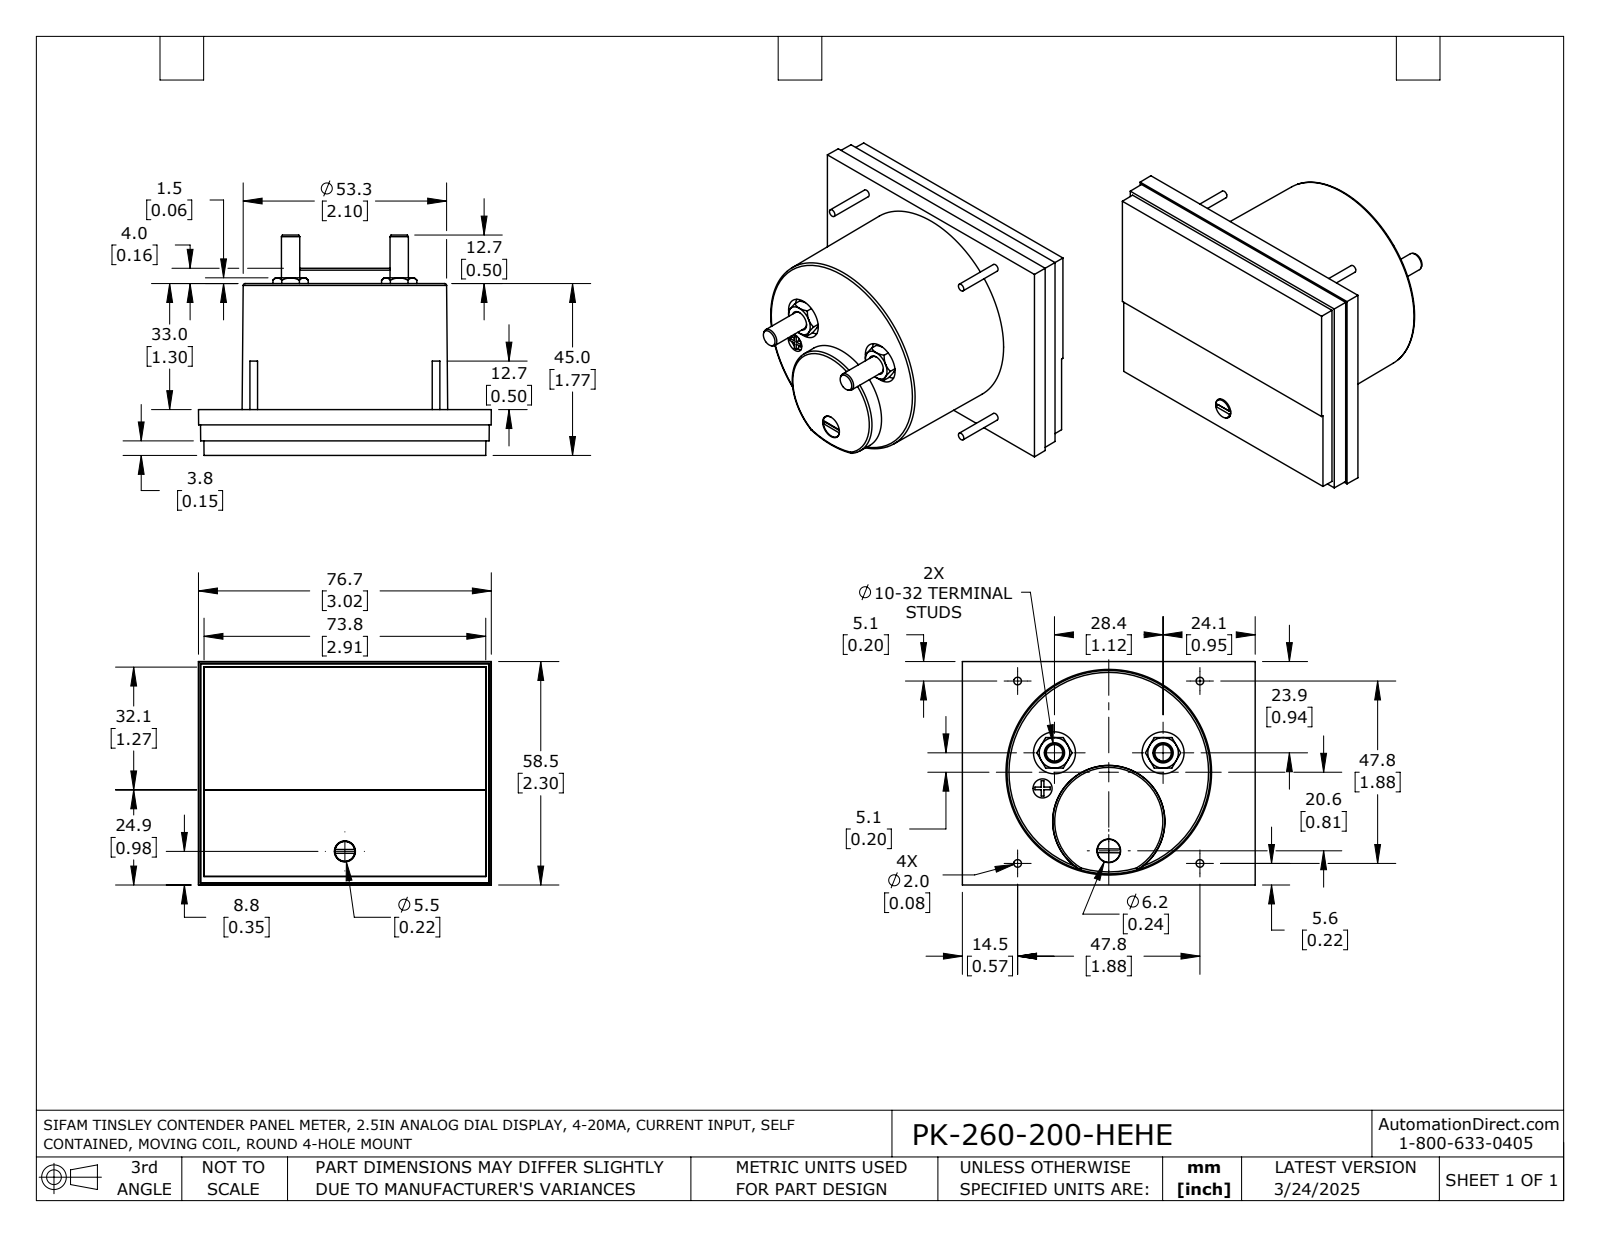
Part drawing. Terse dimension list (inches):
name: PK-260-200-HEHE
written by: SolidWorks 2021 (AUTOMOTIVE_DESIGN)
unit: in
bodies: 1 solid, 192 faces (95 planar, 37 cylindrical, 60 other)
size: 3.02 × 2.303 × 2.272
volume: 7.657 in³; area: 36.55 in²
holes: 3× ⌀0.197, 2× ⌀0.433, 1× ⌀0.209, 1× ⌀0.217, 1× ⌀0.244
bosses: 4× ⌀0.079, 2× ⌀0.189, 1× ⌀0.236, 1× ⌀0.205
rounds: 1× R0.033
face distances: 0.02, 0.472, 0.13, 0.322, 0.15, 0.453, 0.057, 0.077, 0.396, 0.073
hole spacings: 1.155, 1.16, 0.387, 0.938, 0.942, 1.12, 1.295
